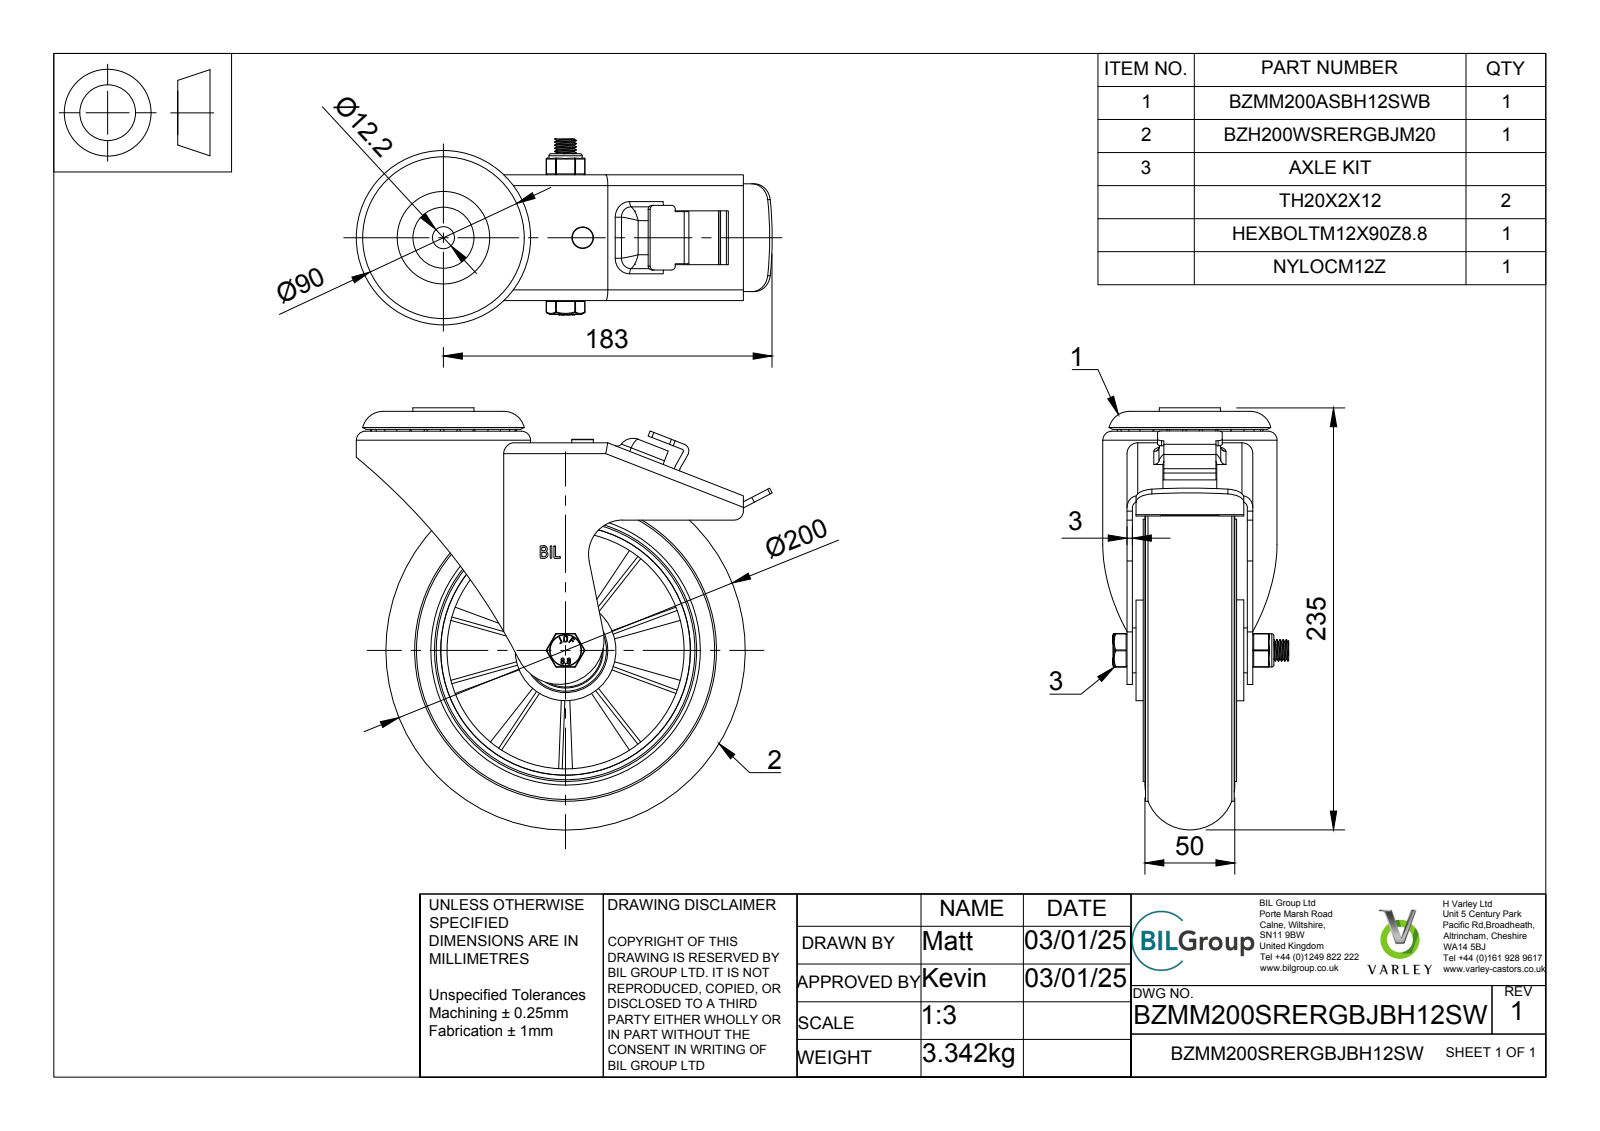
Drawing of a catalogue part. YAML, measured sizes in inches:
part_name: "BZMM200SRERGBJBH12SW v3; BZMM200ASBH12SWB - 64 v1; ZINC PLATED, PRESSED STEEL HEAD; ZINC PLATED, PRESSED STEEL HEAD Geometry (+8 more)"
step_written_by: "Autodesk Translation Framework v13.20.0.188 (AP242_MANAGED_MODEL_BASED_3D_ENGINEERING_MIM_LF)"
units: inches
bodies: {solids: 87, faces: 1506, planar: 638, cylindrical: 330, other: 538}
overall_size: [9.252, 9.114, 4.075]
volume: 66.82
surface_area: 587.3
round_holes:
  - {diameter: 0.48, count: 2}
  - {diameter: 0.236, count: 1}
  - {diameter: 0.276, count: 1}
  - {diameter: 0.394, count: 1}
  - {diameter: 0.472, count: 1}
  - {diameter: 0.484, count: 1}
  - {diameter: 0.551, count: 1}
  - {diameter: 0.787, count: 1}
  - {diameter: 1.122, count: 1}
  - {diameter: 1.213, count: 1}
  - {diameter: 1.587, count: 1}
  - {diameter: 1.594, count: 1}
round_bosses_or_shafts:
  - {diameter: 0.945, count: 2}
  - {diameter: 6.614, count: 1}
  - {diameter: 5.748, count: 1}
  - {diameter: 3.819, count: 1}
  - {diameter: 3.071, count: 1}
  - {diameter: 2.213, count: 1}
  - {diameter: 2.205, count: 1}
  - {diameter: 1.606, count: 1}
partial_cylinders:
  - {radius: 0.059, count: 30}
  - {radius: 0.02, count: 25}
  - {radius: 0.01, count: 12}
  - {radius: 0.03, count: 10}
  - {radius: 0.079, count: 10}
  - {radius: 0.118, count: 6}
  - {radius: 0.128, count: 6}
  - {radius: 0.197, count: 5}
face_to_face_distances: [0.118, 2.638, 0.079, 0.561, 1.88, 0.197, 0.276, 0.394, 1.319, 0.679]
hole_center_spacings: [3.051]
